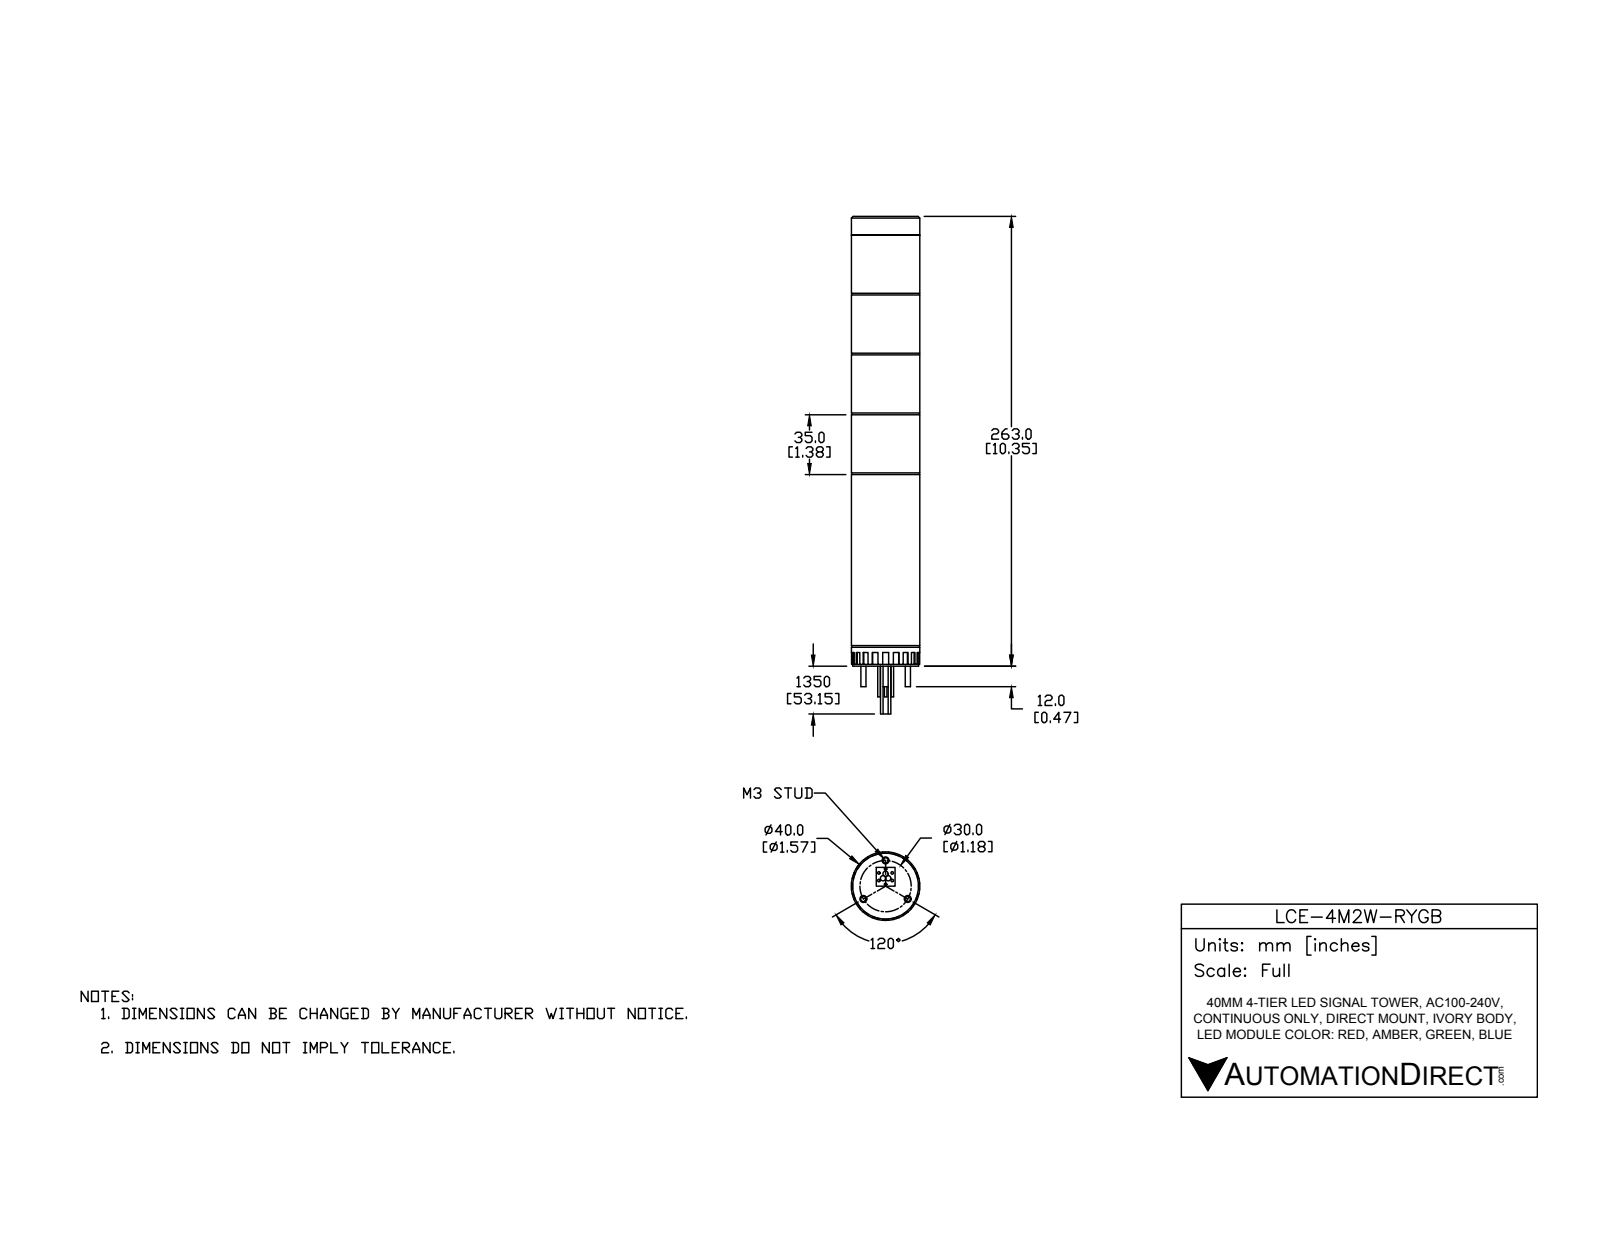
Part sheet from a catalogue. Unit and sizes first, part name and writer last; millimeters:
Units: millimetres
Overall size (bounding box): 291 × 40 × 40
Round holes (diameter × count): ⌀4 ×3, ⌀8 ×1
Round bosses / shafts (diameter × count): ⌀3 ×6, ⌀1.5 ×6, ⌀40 ×1, ⌀39.5 ×1, ⌀38.5 ×1, ⌀5.5 ×1
Main face-to-face distances: 35, 1, 70, 34, 105, 36, 69, 104, 71, 101
Hole centre spacings: 15, 25.98
Volume: 329 689 mm³ · Surface area: 67 680 mm²
Bodies: 26 solids, 222 faces (158 planar, 60 cylindrical, 4 other)
Part name (STEP PRODUCT): LCE-4M2W-RYGB
STEP written by: SolidWorks 2016 (AUTOMOTIVE_DESIGN)
